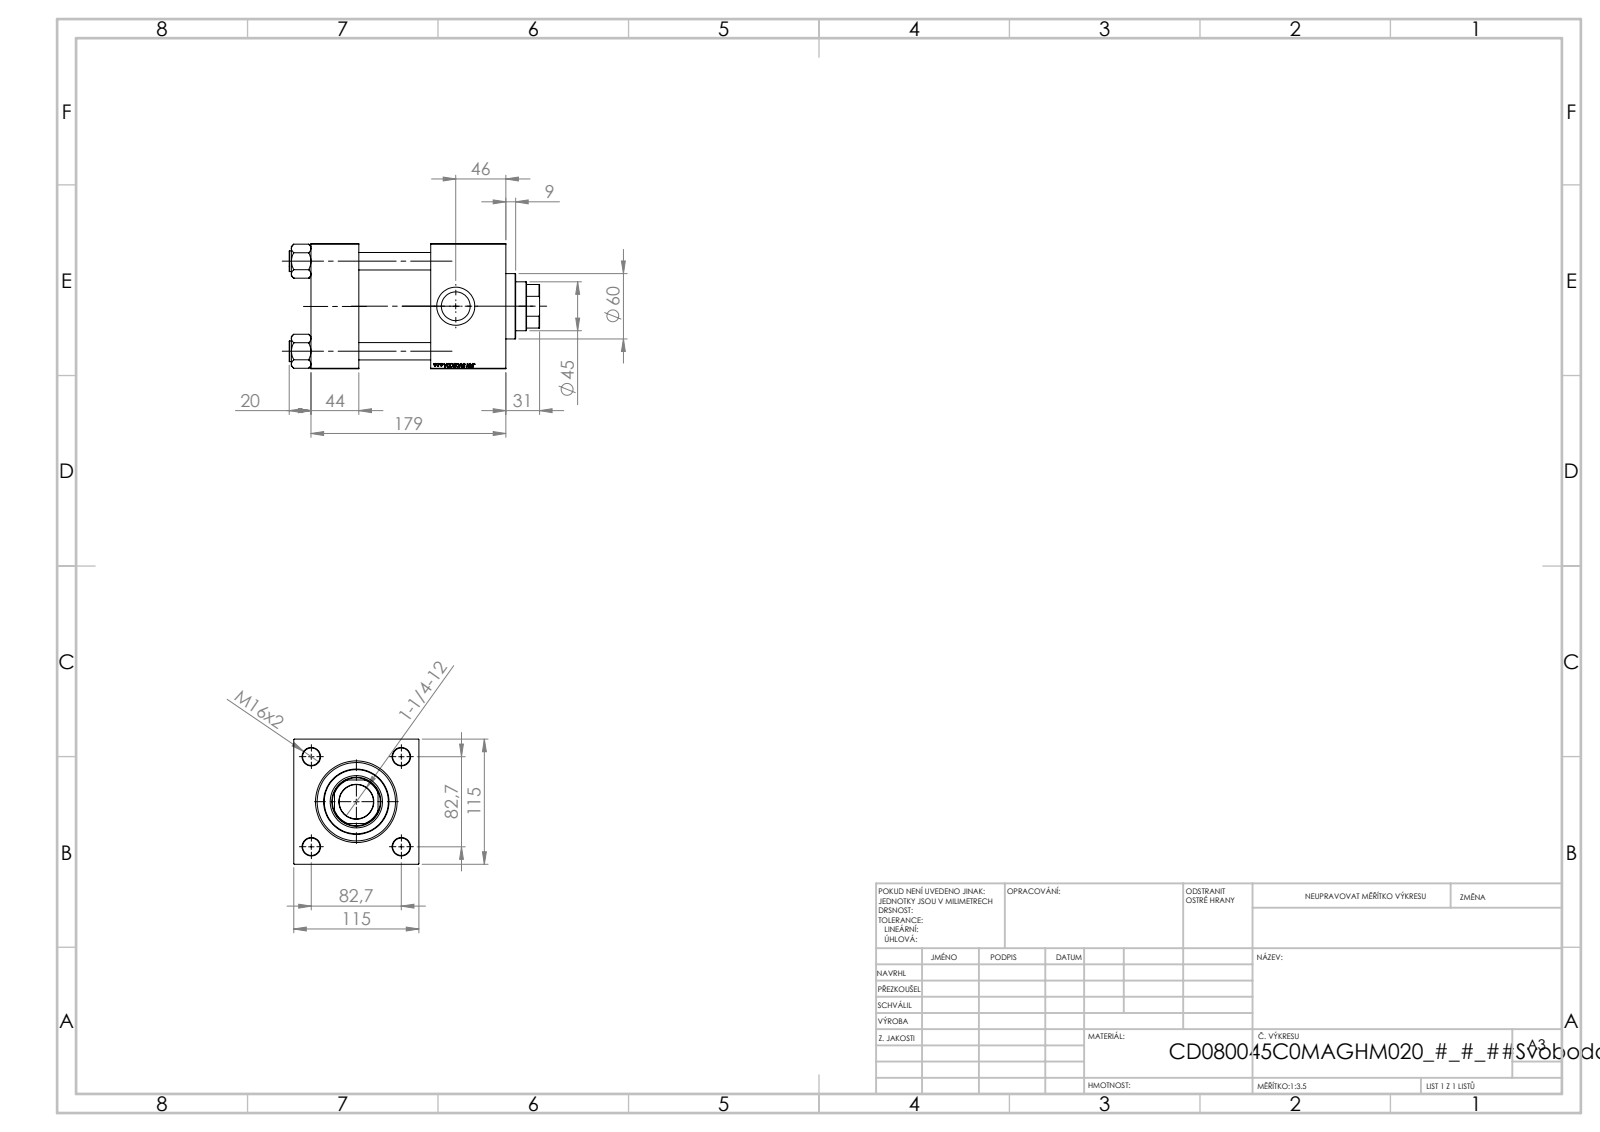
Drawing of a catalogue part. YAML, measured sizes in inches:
part_name: "V215CD_VCP_C; V215CD_C_TYCINKA; V215CD_VC_C; NUT_M5_V215CD_C (+1 more)"
step_written_by: "SolidWorks 2019 (CONFIG_CONTROL_DESIGN)"
units: inches
bodies: {solids: 11, faces: 1197, planar: 574, cylindrical: 87, other: 536}
overall_size: [9.055, 4.528, 4.528]
volume: 111
surface_area: 424.5
round_holes:
  - {diameter: 0.63, count: 4}
  - {diameter: 0.276, count: 2}
  - {diameter: 1.041, count: 2}
  - {diameter: 1.378, count: 2}
  - {diameter: 1.24, count: 1}
  - {diameter: 1.772, count: 1}
  - {diameter: 1.89, count: 1}
  - {diameter: 2.402, count: 1}
  - {diameter: 2.835, count: 1}
  - {diameter: 3.15, count: 1}
round_bosses_or_shafts:
  - {diameter: 0.748, count: 4}
  - {diameter: 3.386, count: 1}
  - {diameter: 2.362, count: 1}
partial_cylinders:
  - {radius: 0.866, count: 1}
face_to_face_distances: [4.528, 1.732, 4.331, 7.047, 5.315, 2.598, 2.717, 0.787, 5.917, 4.185]
hole_center_spacings: [2.302, 3.256, 4.605]
